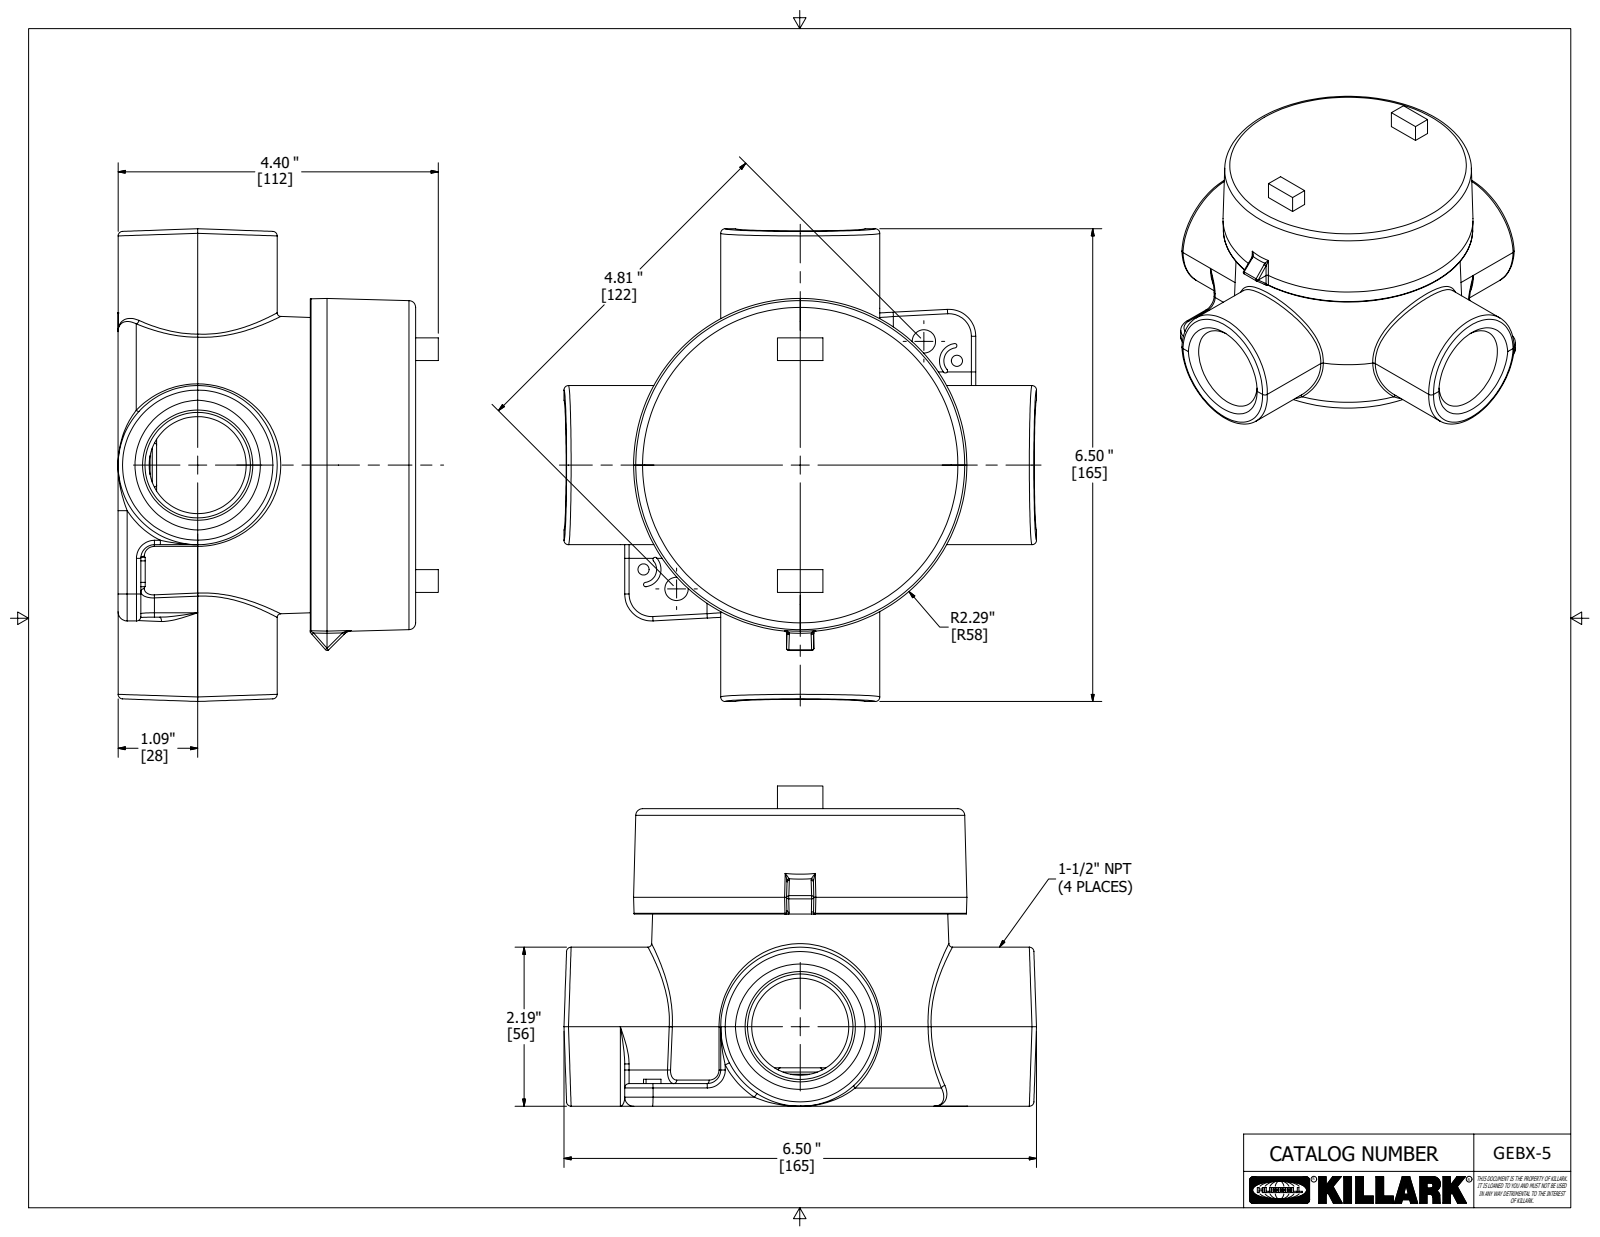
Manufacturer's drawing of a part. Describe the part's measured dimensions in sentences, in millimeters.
The part is named "GEBX-5; 21154; 21147-override". Its 3-D file was written by "Autodesk Inventor 2020 (AUTOMOTIVE_DESIGN)". It is 2 solids with 862 faces: 425 planar, 95 cylindrical and 342 other. Overall it measures 165.1 by 165.1 by 111.9 millimeters. Its volume is 581 400 cubic millimeters and its surface area 146 200 square millimeters. Round holes: 2 of diameter 3.9, 2 of diameter 8.2, 2 of diameter 39.6, 1 of diameter 97.1, 1 of diameter 102.7. Round bosses or shafts: 2 of diameter 55.6. Partial cylindrical surfaces (rounded edges, fillets, slot ends): 36 of radius 1.5, 14 of radius 0.8, 4 of radius 3.2, 4 of radius 4.7, 3 of radius 0.8, 2 of radius 4.6, 2 of radius 6.1, 2 of radius 9.4. The main face-to-face distances are 104, 92.8, 11.1, 88.9, 3.9, 15.1, 67.2, 21.7, 25.7, 36.8. The hole center spacings are 13.4, 61.1, 65.8, 126.2, 122.2, 131.5.
